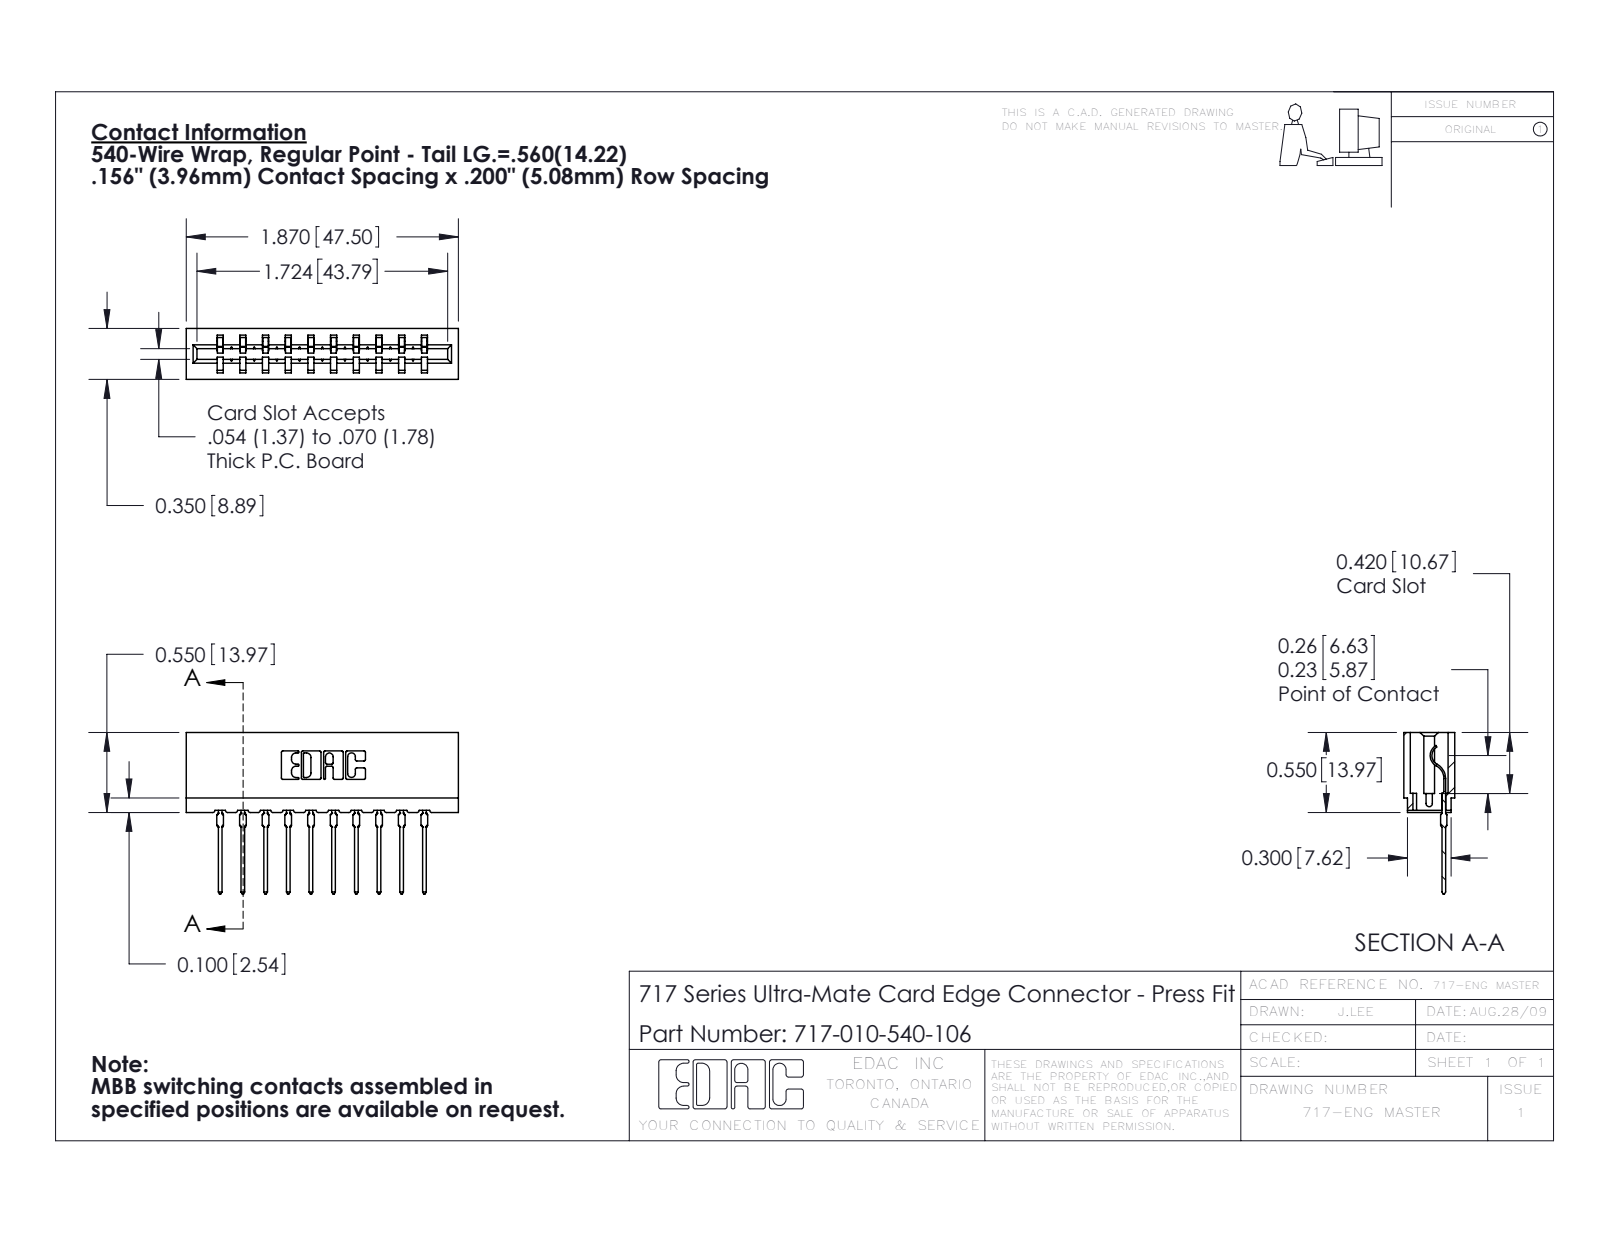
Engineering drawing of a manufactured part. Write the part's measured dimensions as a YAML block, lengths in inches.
part_name: "745-292-001_540; 717-010-540-106; 717 Part_Insulator Option - 06"
step_written_by: "SolidWorks 2016 (CONFIG_CONTROL_DESIGN)"
units: inches
bodies: {solids: 11, faces: 1224, planar: 734, cylindrical: 230, other: 260}
overall_size: [1.87, 1.109, 0.35]
volume: 0.255
surface_area: 8.739
partial_cylinders:
  - {radius: 0.01, count: 22}
  - {radius: 0.015, count: 20}
  - {radius: 0.021, count: 20}
  - {radius: 0.007, count: 6}
  - {radius: 0.031, count: 6}
  - {radius: 0.005, count: 4}
  - {radius: 0.011, count: 4}
  - {radius: 0.026, count: 3}
face_to_face_distances: [0.156, 0.212, 0.138, 0.624, 0.35, 0.468, 0.198, 0.312, 0.354, 0.312]
